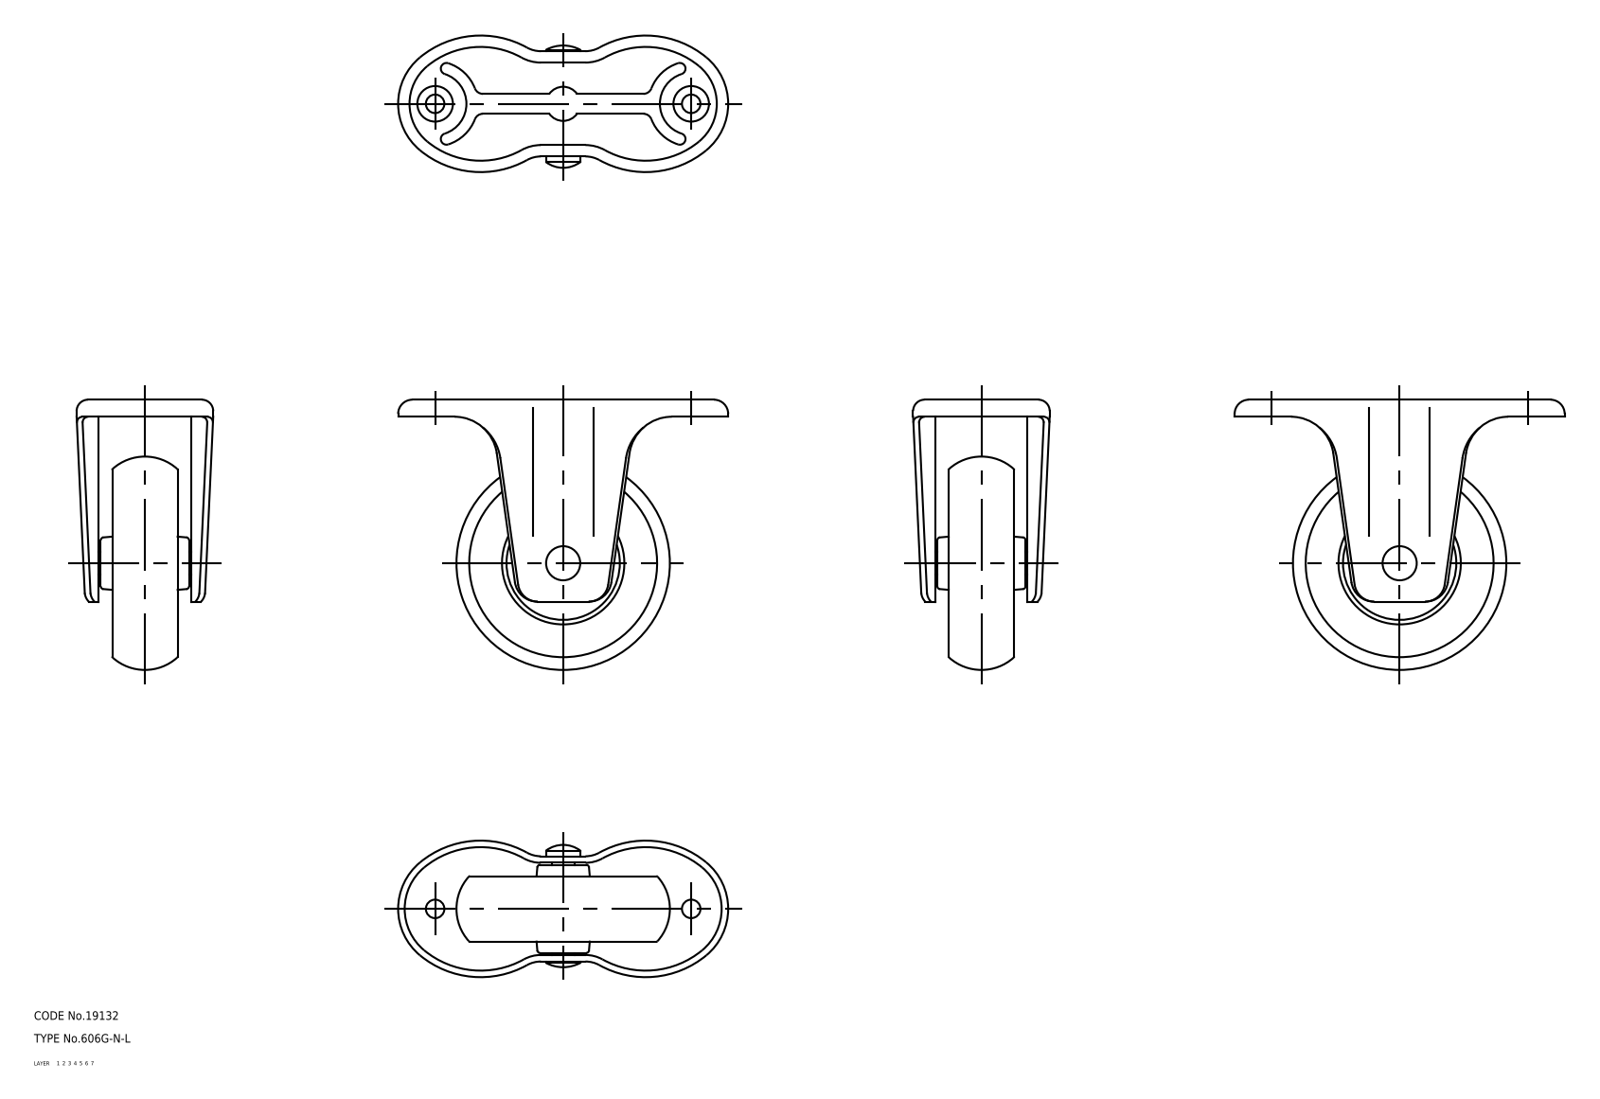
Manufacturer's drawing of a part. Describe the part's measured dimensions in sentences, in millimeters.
The part is named "wheel; axle; No_606G_N_L_16429_36". Its 3-D file was written by "CADfix (AUTOMOTIVE_DESIGN)". It is 3 solids with 185 faces: 0 planar, 0 cylindrical and 185 other. Overall it measures 116 by 95 by 48 millimeters. Its volume is 105 669 cubic millimeters and its surface area 40 879 square millimeters.
